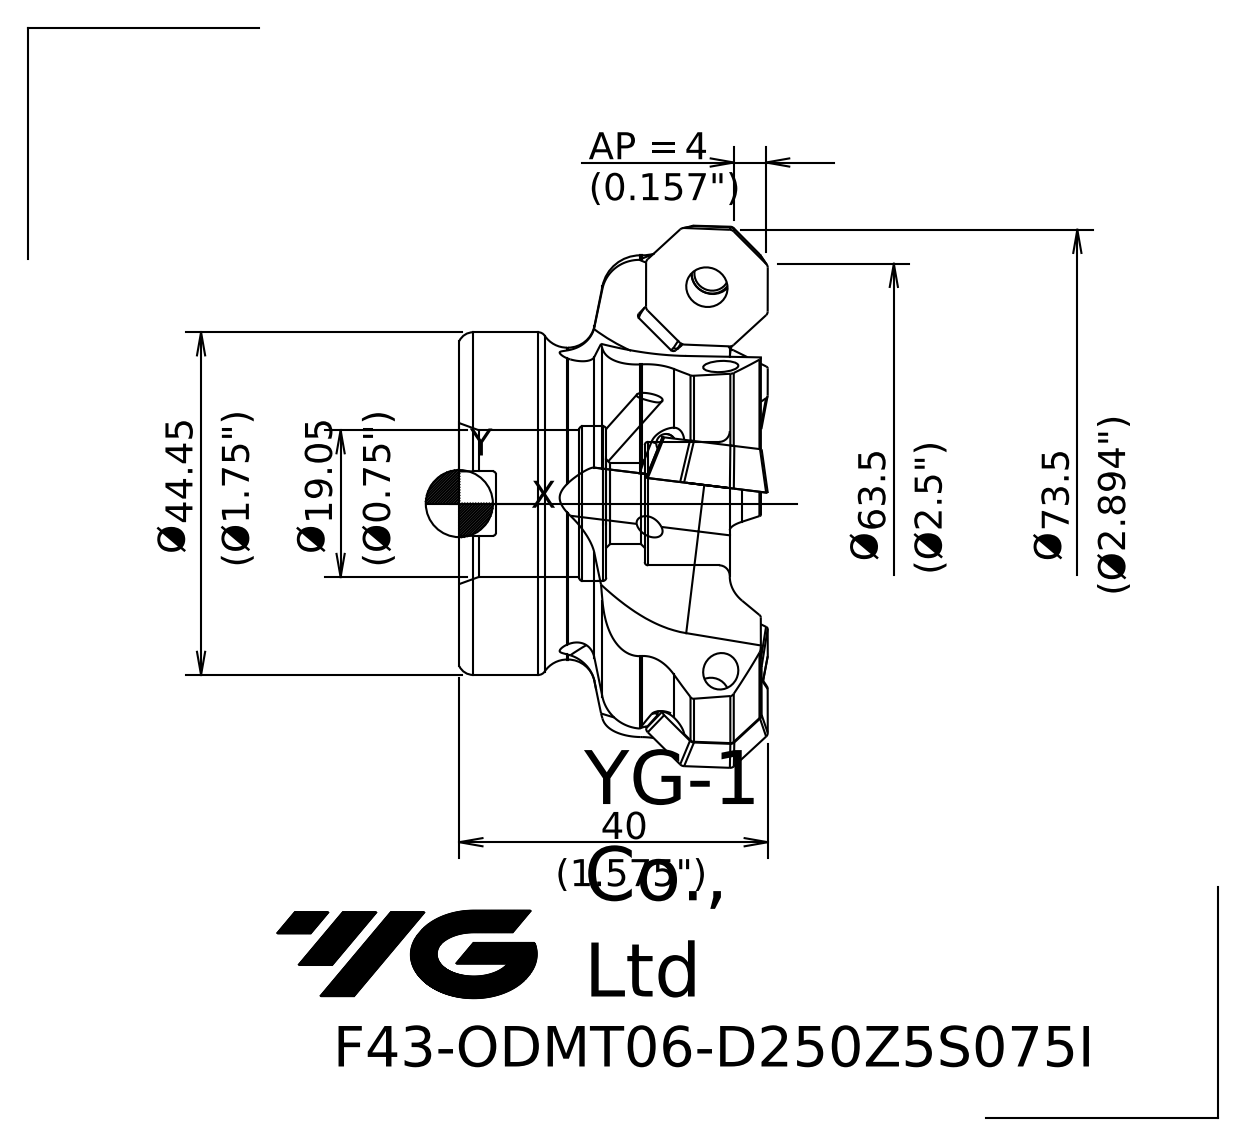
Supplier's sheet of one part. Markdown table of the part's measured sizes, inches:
| quantity | value |
| --- | --- |
| part name | 10224B54D97Bw4jj |
| STEP written by | SIEMENS PLM Software NX 10.0 (AP203_CONFIGURATION_CONTROLLED_3D_DESIGN_OF_MECHANICAL_PARTS_AND_ASSEMBLIES_MIM_LF) |
| units | inches |
| bodies | 1 solid, 65 faces (12 planar, 11 cylindrical, 42 other) |
| overall size | 2.898 × 2.898 × 1.575 |
| volume | 5.138 in³ |
| surface area | 38.68 in² |
| round holes (diameter × count) | 0.413 × 1, 0.63 × 1, 0.75 × 1, 0.789 × 1 |
| round bosses / shafts (diameter × count) | 2.535 × 1, 1.75 × 1, 1.593 × 1 |
| partial cylindrical surfaces (radius × count) | 0.016 × 2 |
| main face-to-face distances | 1.381, 1.194, 0.187, 0.631, 0.563, 0.75, 0.329, 0.434, 0.197, 0.76 |
